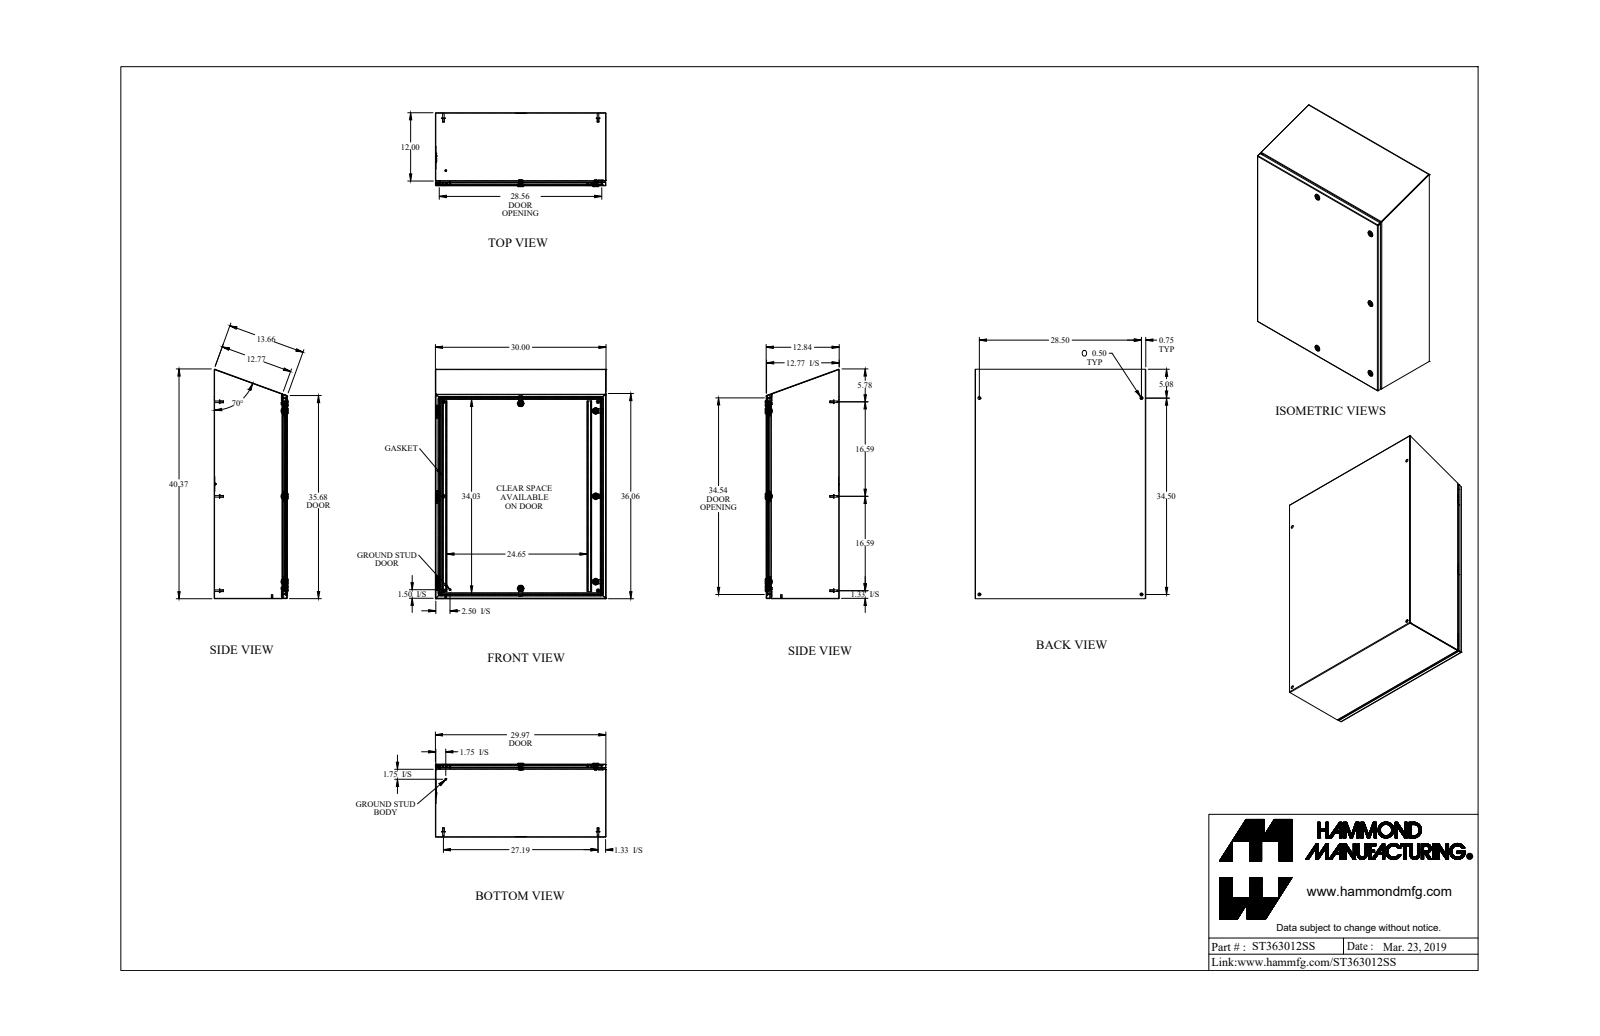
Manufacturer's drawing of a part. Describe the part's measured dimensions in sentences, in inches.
The part is named "ST363012SS". Its 3-D file was written by "SolidWorks 2018 (AUTOMOTIVE_DESIGN)". It is 50 solids with 1236 faces: 681 planar, 377 cylindrical and 178 other. Overall it measures 40.328 by 30 by 12.997 inches. Its volume is 321.6 cubic inches and its surface area 8 998 square inches. Round holes: 9 of diameter 0.5, 5 of diameter 0.197, 5 of diameter 0.387, 5 of diameter 0.63, 5 of diameter 0.768, 1 of diameter 0.172, 1 of diameter 0.24, 1 of diameter 0.242. Round bosses or shafts: 9 of diameter 0.625, 8 of diameter 0.313, 6 of diameter 0.275, 5 of diameter 1.1, 5 of diameter 0.785, 5 of diameter 0.525, 5 of diameter 0.236, 2 of diameter 0.625. Partial cylindrical surfaces (rounded edges, fillets, slot ends): 18 of radius 0.036, 18 of radius 0.108, 12 of radius 0.01, 12 of radius 0.048, 10 of radius 0.125, 6 of radius 0.006, 6 of radius 0.062, 5 of radius 0.188. The main face-to-face distances are 0.072, 12.765, 12.693, 12.837, 29.928, 29.856, 30, 0.837, 11.928, 0.909. The hole center spacings are 15, 27.519, 28.5, 34.5, 44.749, 2.492, 2.494, 13.242.
